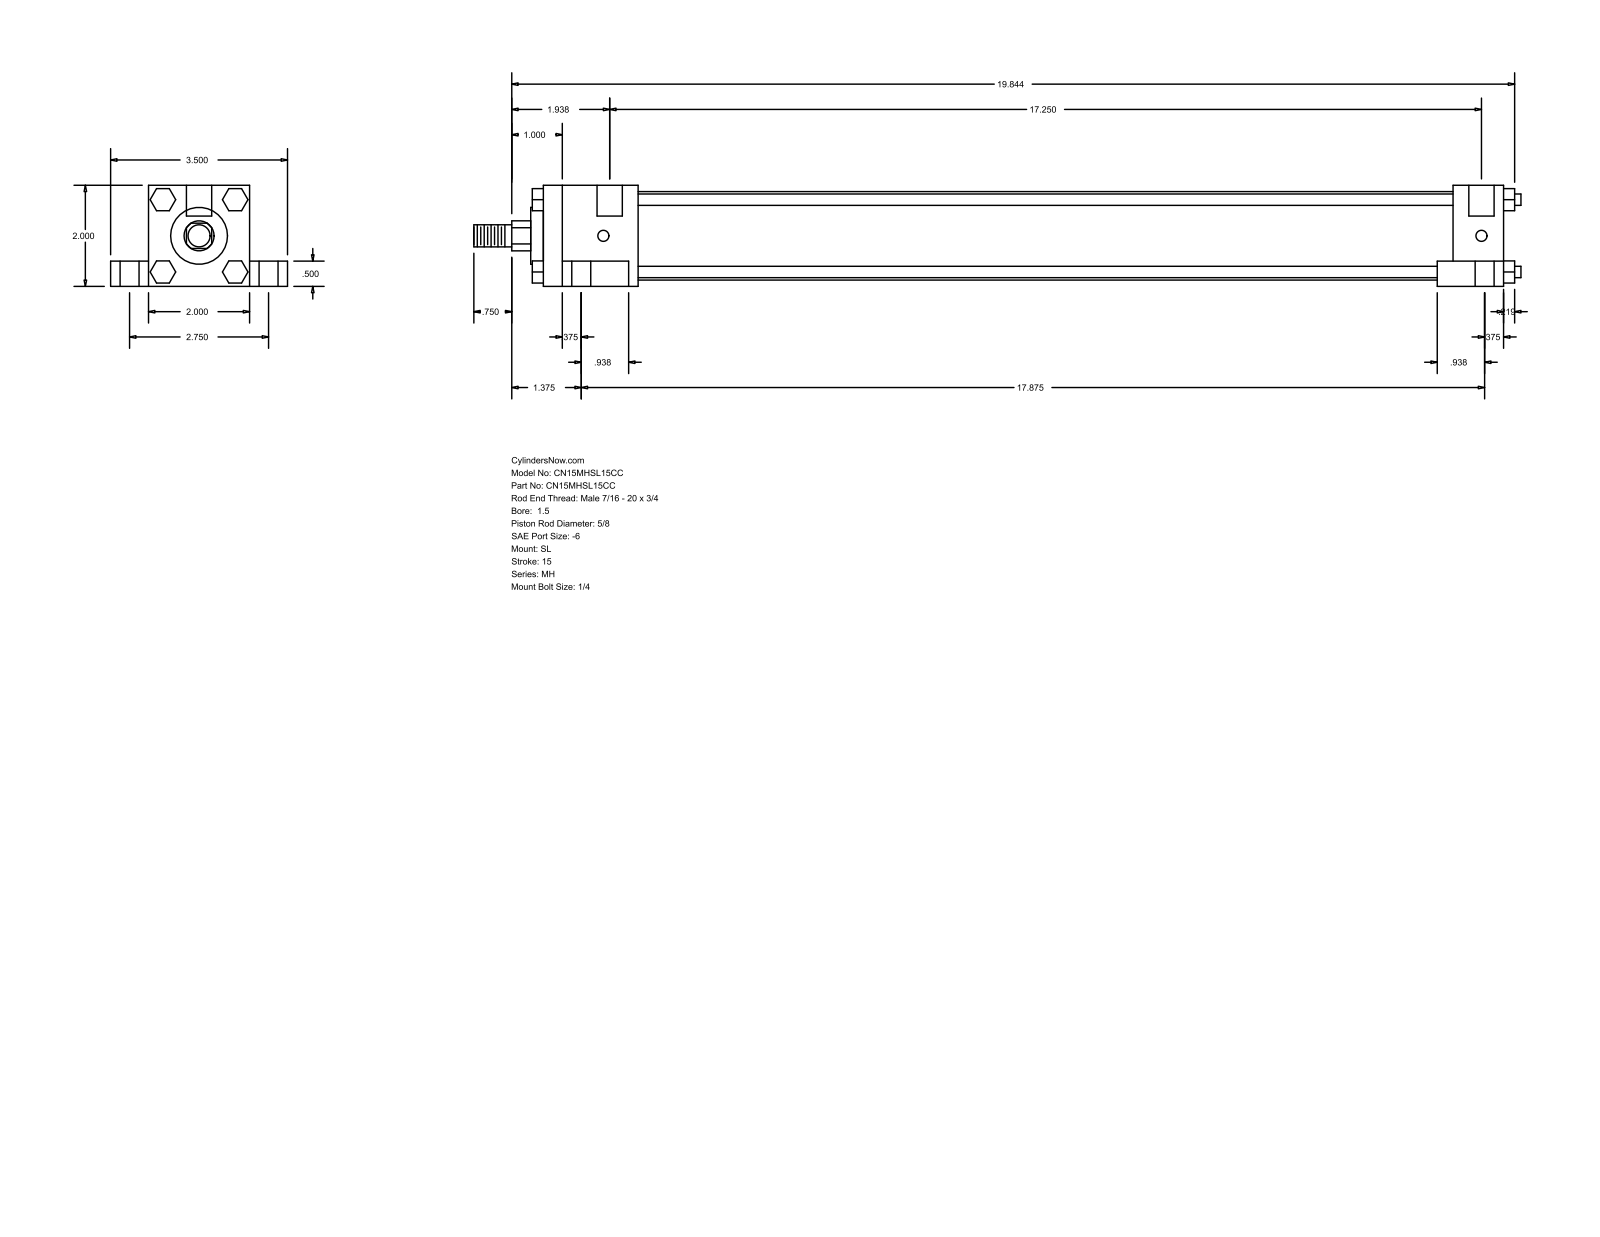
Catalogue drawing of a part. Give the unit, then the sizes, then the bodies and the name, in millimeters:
Units: millimetres
Overall size (bounding box): 526.26 × 88.9 × 50.8
Round holes (diameter × count): ⌀5.56 ×4, ⌀9.53 ×4, ⌀15.88 ×4, ⌀12.7 ×2
Round bosses / shafts (diameter × count): ⌀5.71 ×4, ⌀44.45 ×1, ⌀28.57 ×1, ⌀15.88 ×1, ⌀11.11 ×1
Partial cylindrical surfaces — rounded edges, fillets, slot ends (radius × count): R7.54 ×1
Main face-to-face distances: 50.8, 38.1, 19.05, 12.7, 69.85, 482.6, 9.52, 33.34, 439.74, 457.19
Hole centre spacings: 34.96, 36.65, 37.73, 69.84, 441.12, 441.32, 444.28, 453.79
Bodies: 0 solids, 148 faces (112 planar, 36 cylindrical, 0 other)
Part name (STEP PRODUCT): MH_SL__0150_0.625
STEP written by: GSSL Pune (CONFIG_CONTROL_DESIGN)
